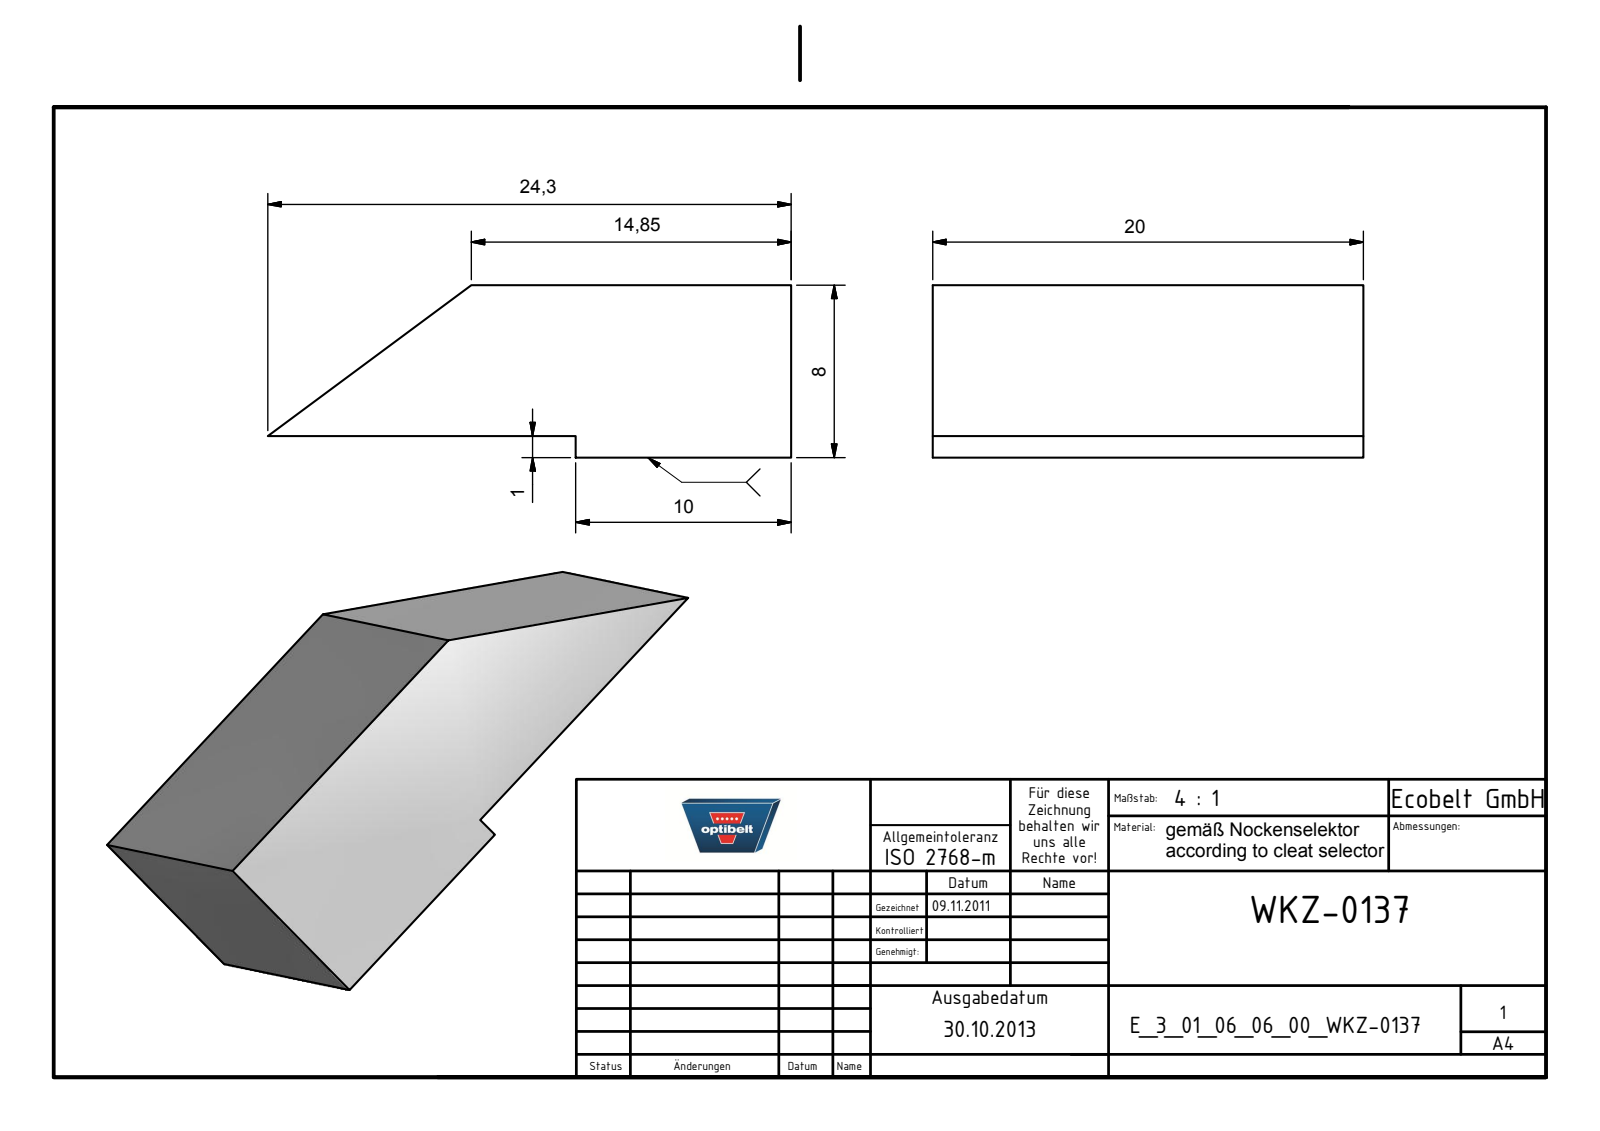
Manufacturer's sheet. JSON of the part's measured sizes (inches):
{"part_name": "E_3_01_06_06_00_WKZ-0137", "step_written_by": "Autodesk Inventor 2025 (AUTOMOTIVE_DESIGN)", "units": "inches", "bodies": {"solids": 1, "faces": 8, "planar": 8, "cylindrical": 0, "other": 0}, "overall_size": [0.957, 0.787, 0.315], "volume_in3": 0.179, "surface_area_in2": 2.313, "face_to_face_distances": [0.276, 0.039, 0.315, 0.787, 0.394]}
